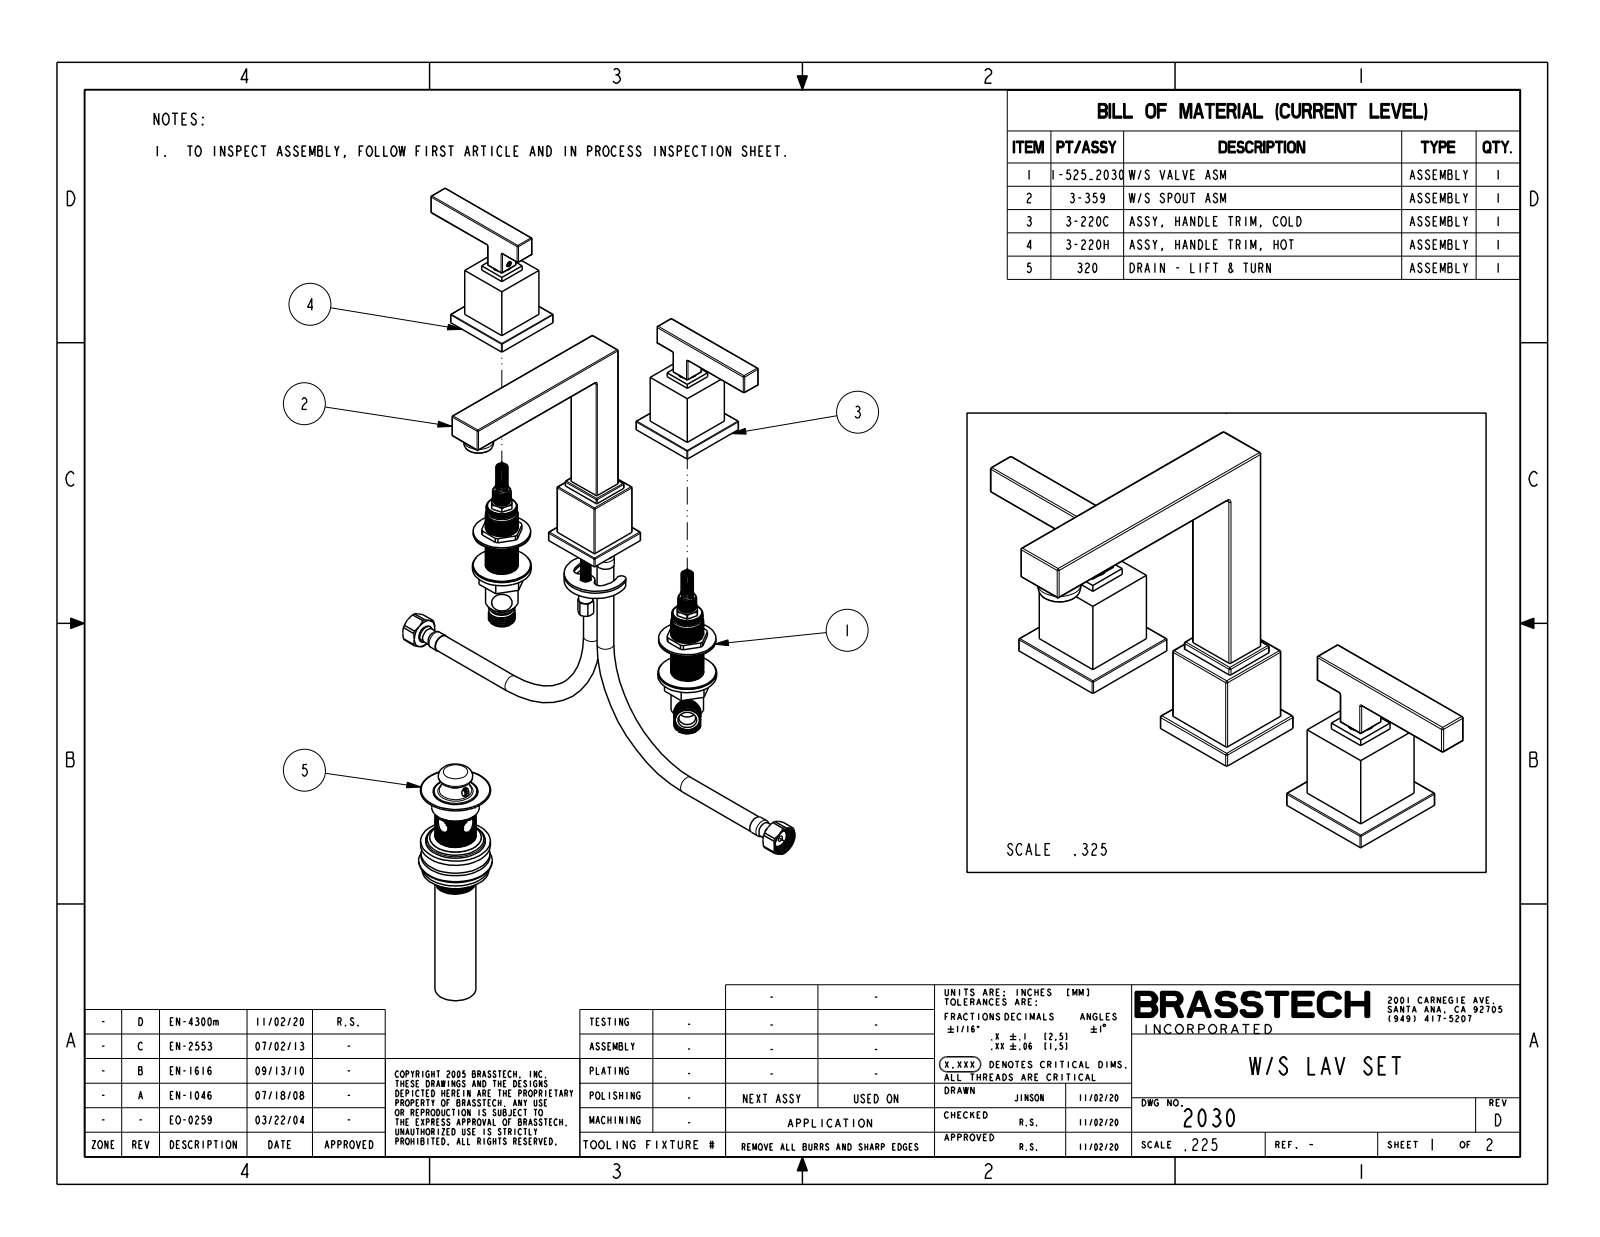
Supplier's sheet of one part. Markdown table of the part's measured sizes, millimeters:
| quantity | value |
| --- | --- |
| part name | 2030 |
| STEP written by | CREO PARAMETRIC BY PTC INC, 2018400 (CONFIG_CONTROL_DESIGN) |
| units | millimeters |
| bodies | 3 solids, 257 faces (79 planar, 114 cylindrical, 64 other) |
| overall size | 343.4 × 182.2 × 170.4 |
| volume | 509 500 mm³ |
| surface area | 86 260 mm² |
| round bosses / shafts (diameter × count) | 20.3 × 2, 10.2 × 2, 23.5 × 1, 22.4 × 1 |
| partial cylindrical surfaces (radius × count) | 0.8 × 75, 0.5 × 14, 2 × 1 |
| main face-to-face distances | 12.4, 28.3, 7.9, 40.6, 8.4, 32.2, 4, 19.8, 28.6, 203.2 |
